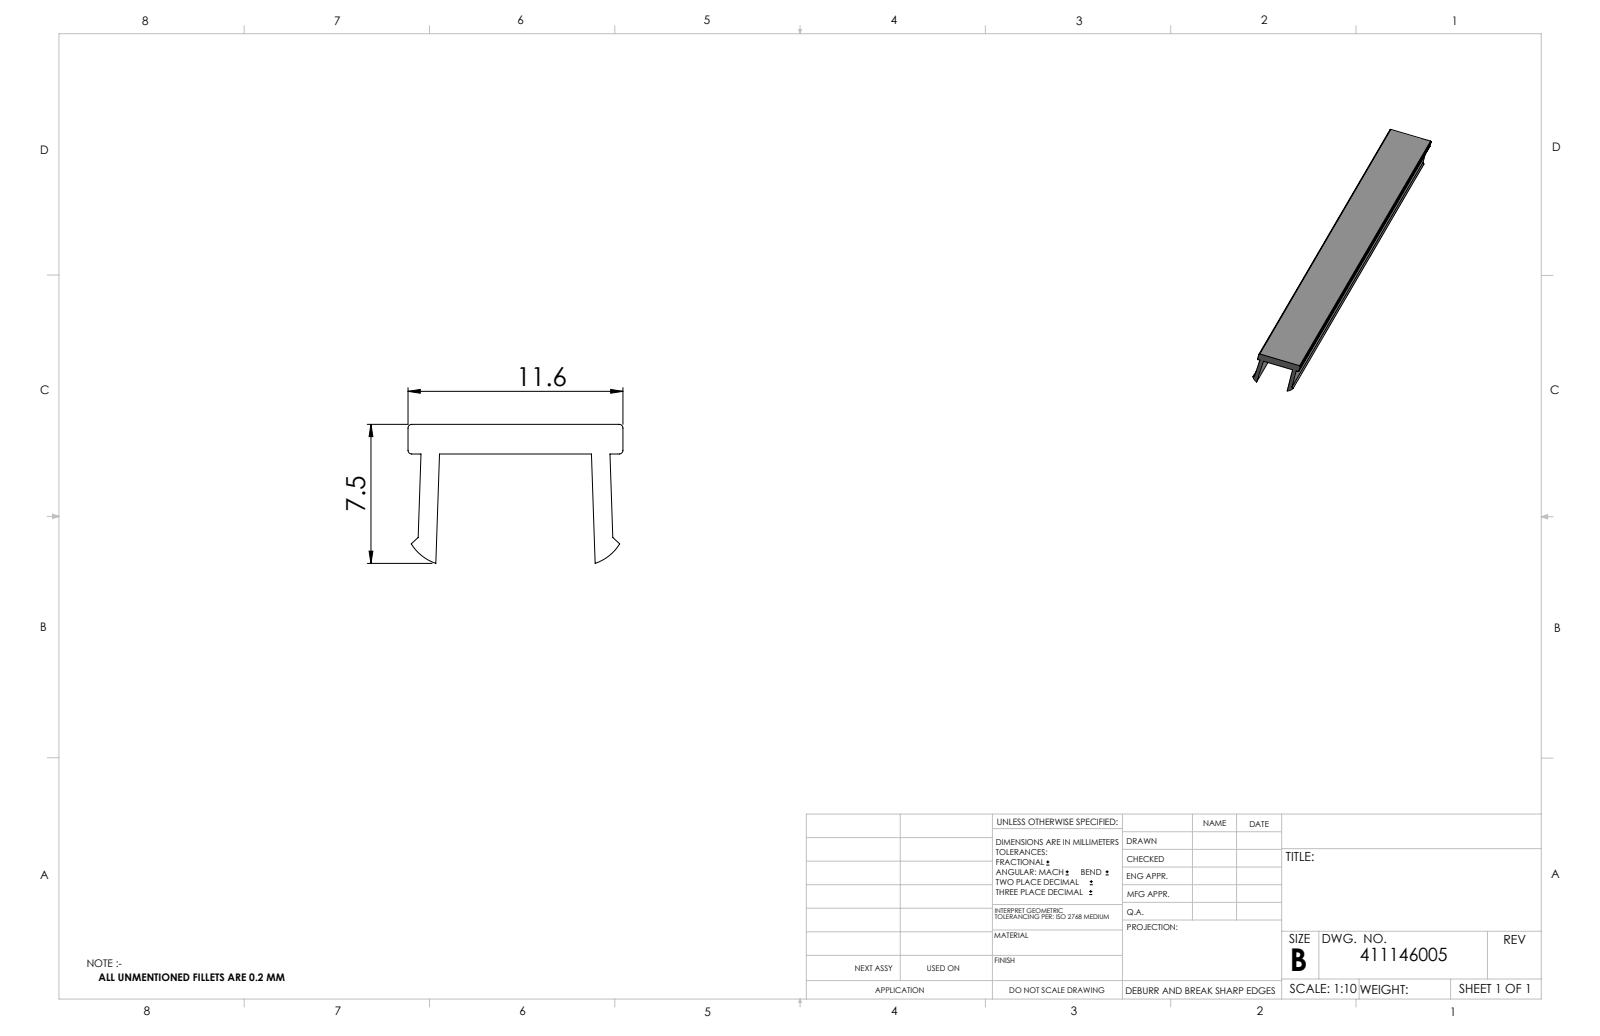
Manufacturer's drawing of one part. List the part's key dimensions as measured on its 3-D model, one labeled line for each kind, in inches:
Part name (STEP PRODUCT): 411146005_c_1
STEP written by: SolidWorks 2014 (CONFIG_CONTROL_DESIGN)
Units: inches
Bodies: 1 solid, 20 faces (14 planar, 6 cylindrical, 0 other)
Overall size (bounding box): 39.37 × 0.457 × 0.295
Volume: 1.838 in³ · Surface area: 76.57 in²
Partial cylindrical surfaces — rounded edges, fillets, slot ends (radius × count): R0.008 ×4, R0.098 ×2
Main face-to-face distances: 0.063, 0.039, 0.457, 39.37
